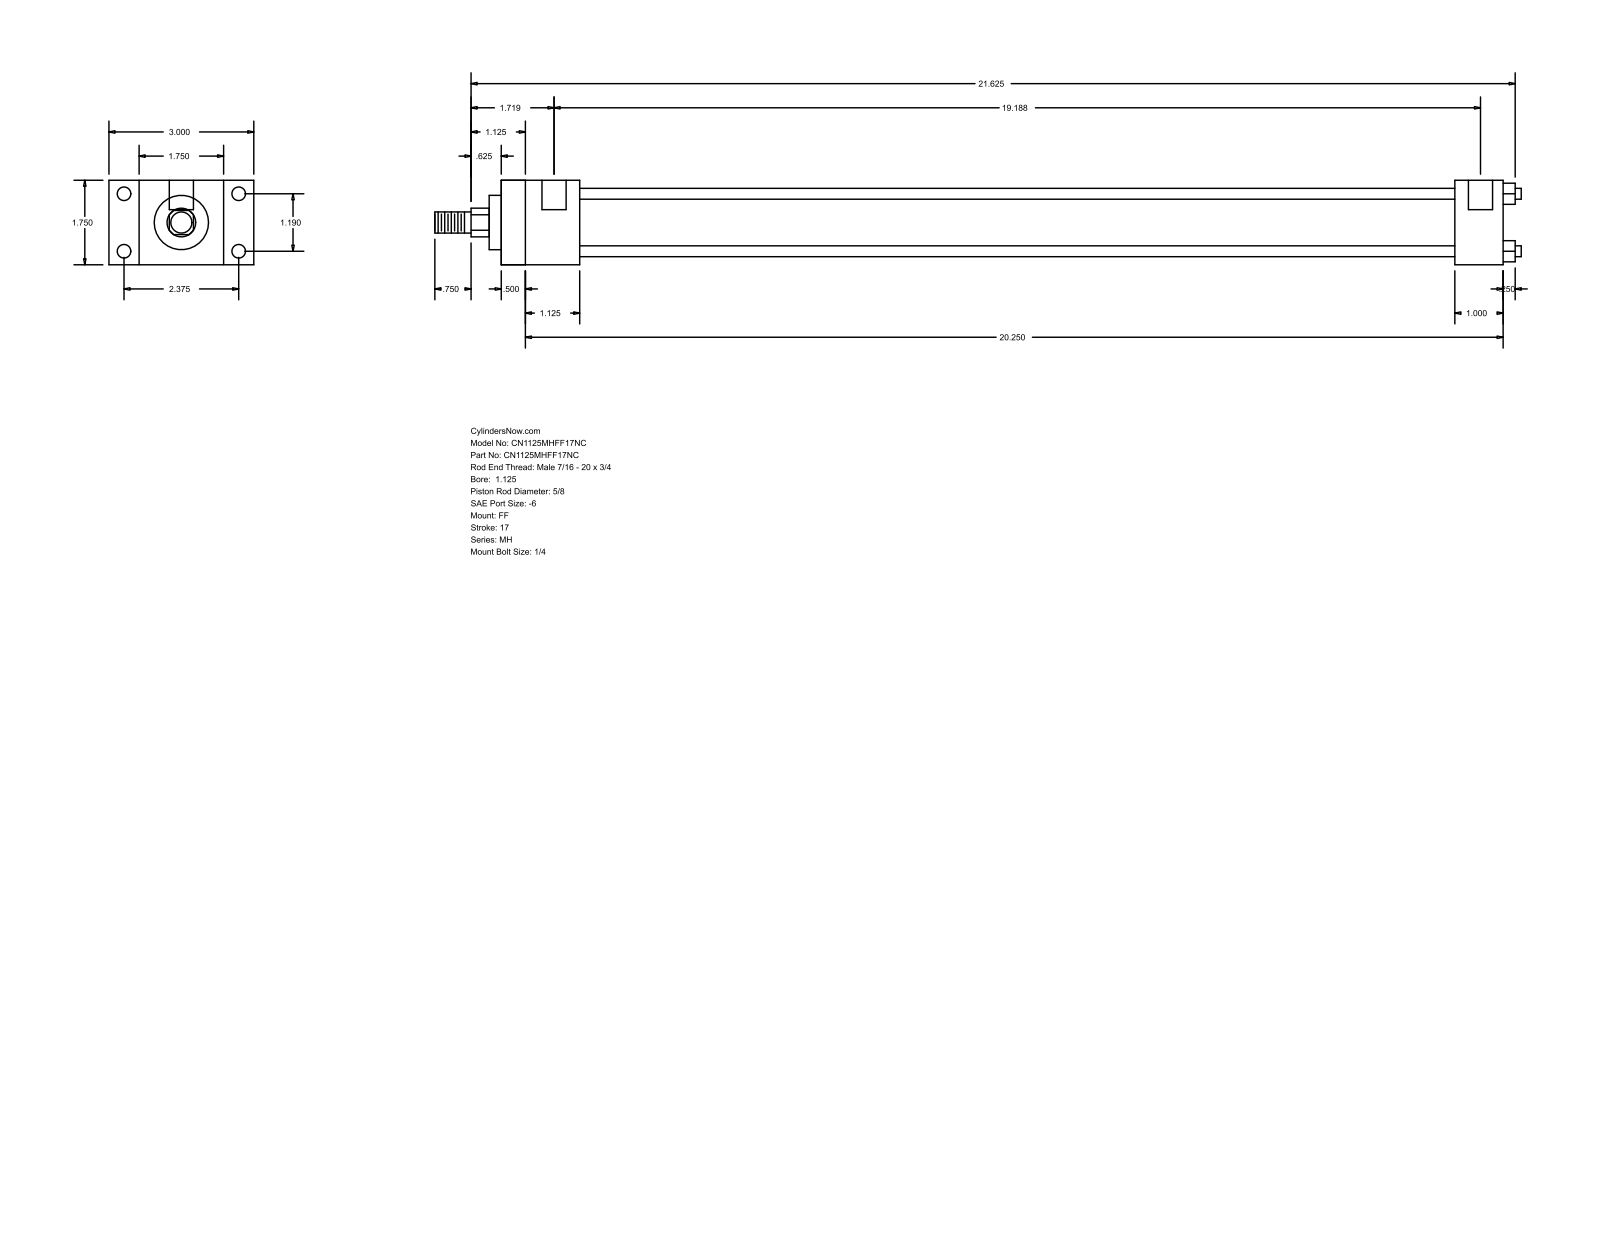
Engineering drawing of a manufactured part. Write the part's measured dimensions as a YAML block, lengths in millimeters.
part_name: "MH_FF__0112_0.625"
step_written_by: "GSSL Pune (CONFIG_CONTROL_DESIGN)"
units: millimeters
bodies: {solids: 0, faces: 92, planar: 64, cylindrical: 28, other: 0}
overall_size: [571.5, 76.2, 44.45]
round_holes:
  - {diameter: 5.56, count: 4}
  - {diameter: 7.14, count: 4}
  - {diameter: 12.7, count: 2}
round_bosses_or_shafts:
  - {diameter: 5.71, count: 4}
  - {diameter: 34.92, count: 1}
  - {diameter: 28.57, count: 1}
  - {diameter: 15.88, count: 1}
  - {diameter: 11.11, count: 1}
partial_cylinders:
  - {radius: 7.54, count: 1}
face_to_face_distances: [44.46, 527.04, 15.87, 12.69, 514.35, 28.58, 60.33, 25.4, 41.27, 501.64]
hole_center_spacings: [30.22, 60.32, 67.47, 484.19, 3.17, 487.36]
